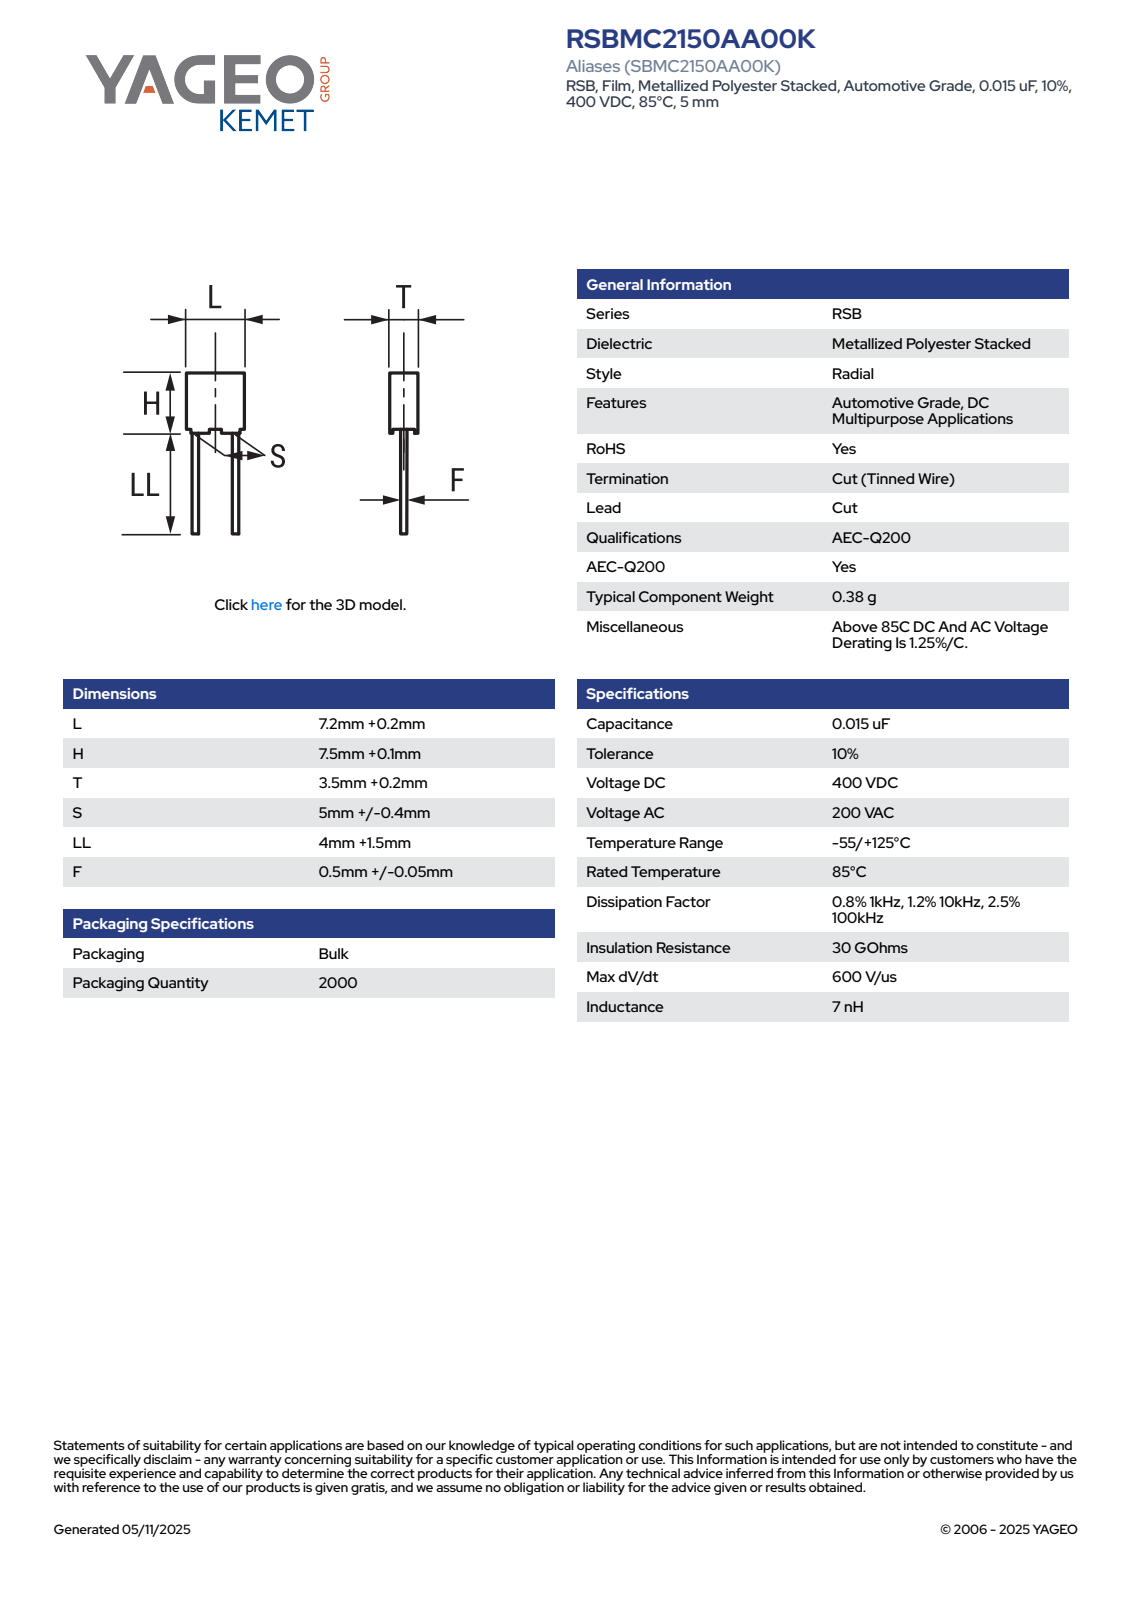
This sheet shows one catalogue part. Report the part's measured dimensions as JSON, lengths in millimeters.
{"part_name": "CFR_RB3_7.2X7.5X3.5_L7.4H7.6T3.7S5LL5.5F0.65", "step_written_by": "SolidWorks 2014 (AUTOMOTIVE_DESIGN)", "units": "millimeters", "bodies": {"solids": 4, "faces": 85, "planar": 77, "cylindrical": 8, "other": 0}, "overall_size": [13.1, 7.4, 3.71], "volume_mm3": 194, "surface_area_mm2": 262, "round_bosses_or_shafts": [[0.65, 2]], "partial_cylinders_radius": [[0.5, 4]], "face_to_face_distances": [3.7, 7.4, 6.85, 3.45, 7.15, 3.2, 0.75, 7.6, 6.9, 3.71]}
